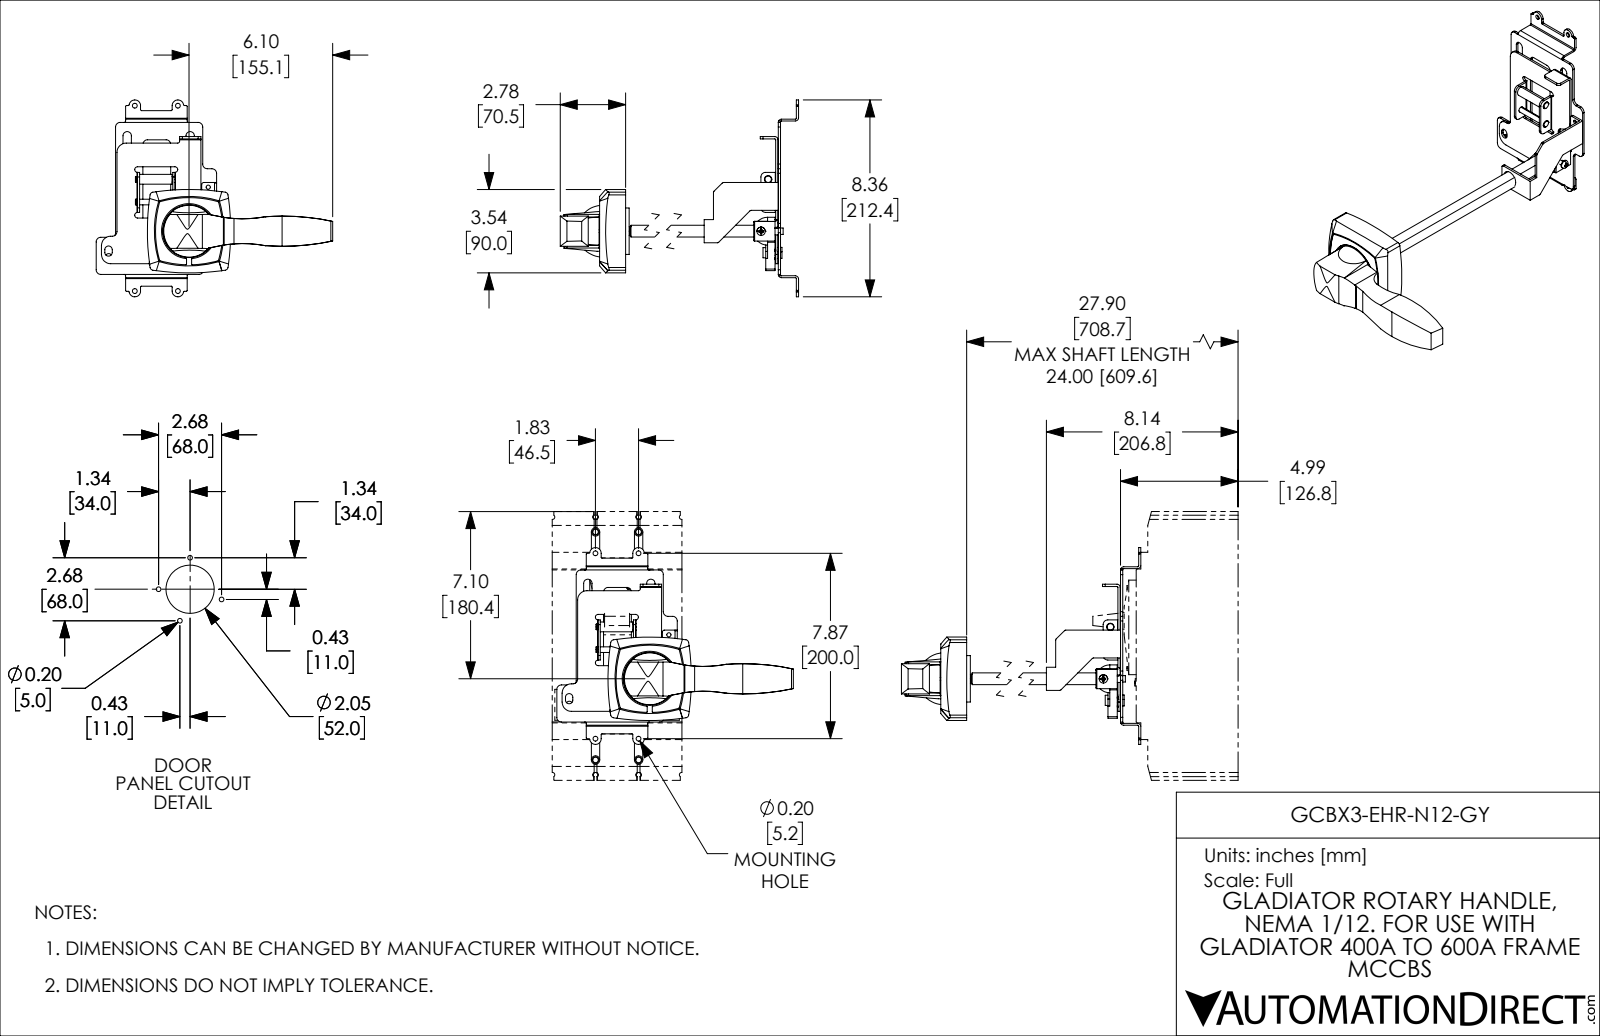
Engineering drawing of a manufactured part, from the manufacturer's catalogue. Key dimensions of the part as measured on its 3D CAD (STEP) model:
Part name (STEP PRODUCT): GCBX3-EHR-N12-GY
STEP written by: SolidWorks 2021 (CONFIG_CONTROL_DESIGN)
Units: millimetres
Bodies: 14 solids, 582 faces (232 planar, 290 cylindrical, 60 other)
Overall size (bounding box): 383.6 × 255.36 × 212.4
Volume: 511 958 mm³ · Surface area: 148 668 mm²
Round holes (diameter × count): ⌀5 ×4, ⌀5.2 ×4, ⌀8 ×3, ⌀3.5 ×2, ⌀4 ×2, ⌀4.5 ×2, ⌀6.2 ×2, ⌀7 ×2, ⌀4.1 ×1, ⌀4.3 ×1, ⌀5.3 ×1, ⌀5.7 ×1
Round bosses / shafts (diameter × count): ⌀5 ×3, ⌀7 ×2, ⌀6 ×2, ⌀3 ×2, ⌀59.5 ×1, ⌀50 ×1, ⌀12 ×1, ⌀11.8 ×1
Partial cylindrical surfaces — rounded edges, fillets, slot ends (radius × count): R1 ×25, R5 ×21, R0.5 ×16, R3 ×11, R2 ×9, R1.5 ×8, R3.5 ×8, R10 ×5
Main face-to-face distances: 2.3, 2.8, 0.5, 5.1, 12.7, 295.2, 292.9, 292.4, 290.1, 23.35
Hole centre spacings: 34, 1.3, 32.09, 33, 33.01, 33.98, 35.74, 35.75
